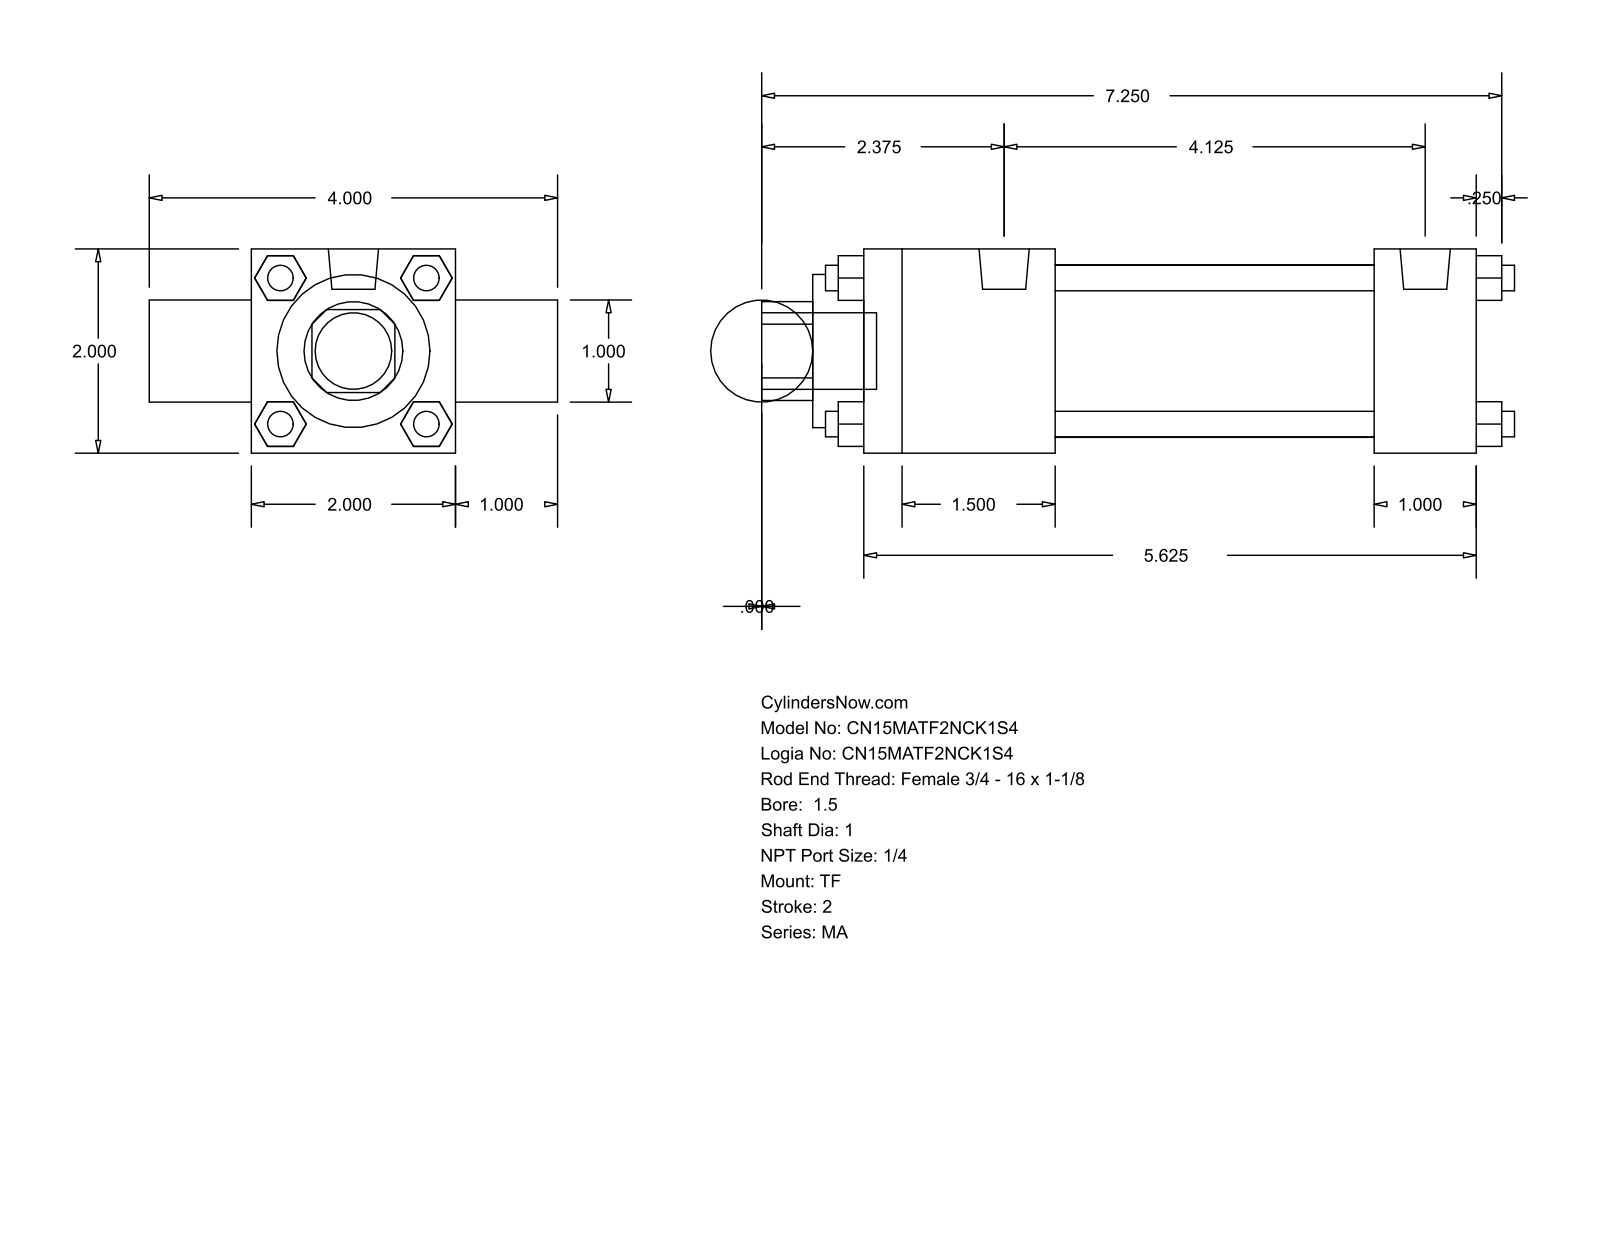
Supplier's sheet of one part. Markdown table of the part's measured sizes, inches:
| quantity | value |
| --- | --- |
| part name | MA_TF__0150_1 |
| STEP written by | GSSL Pune (CONFIG_CONTROL_DESIGN) |
| units | inches |
| bodies | 0 solids, 120 faces (92 planar, 28 cylindrical, 0 other) |
| overall size | 7.375 × 4 × 2 |
| round holes (diameter × count) | 1 × 2, 1.5 × 1, 1.69 × 1 |
| round bosses / shafts (diameter × count) | 0.25 × 4, 0.313 × 3, 0.492 × 2, 0.75 × 1 |
| partial cylindrical surfaces (radius × count) | 0.484 × 1 |
| main face-to-face distances | 2, 1, 6, 3, 0.25, 1.875, 5, 3.125, 4.125, 6.5 |
